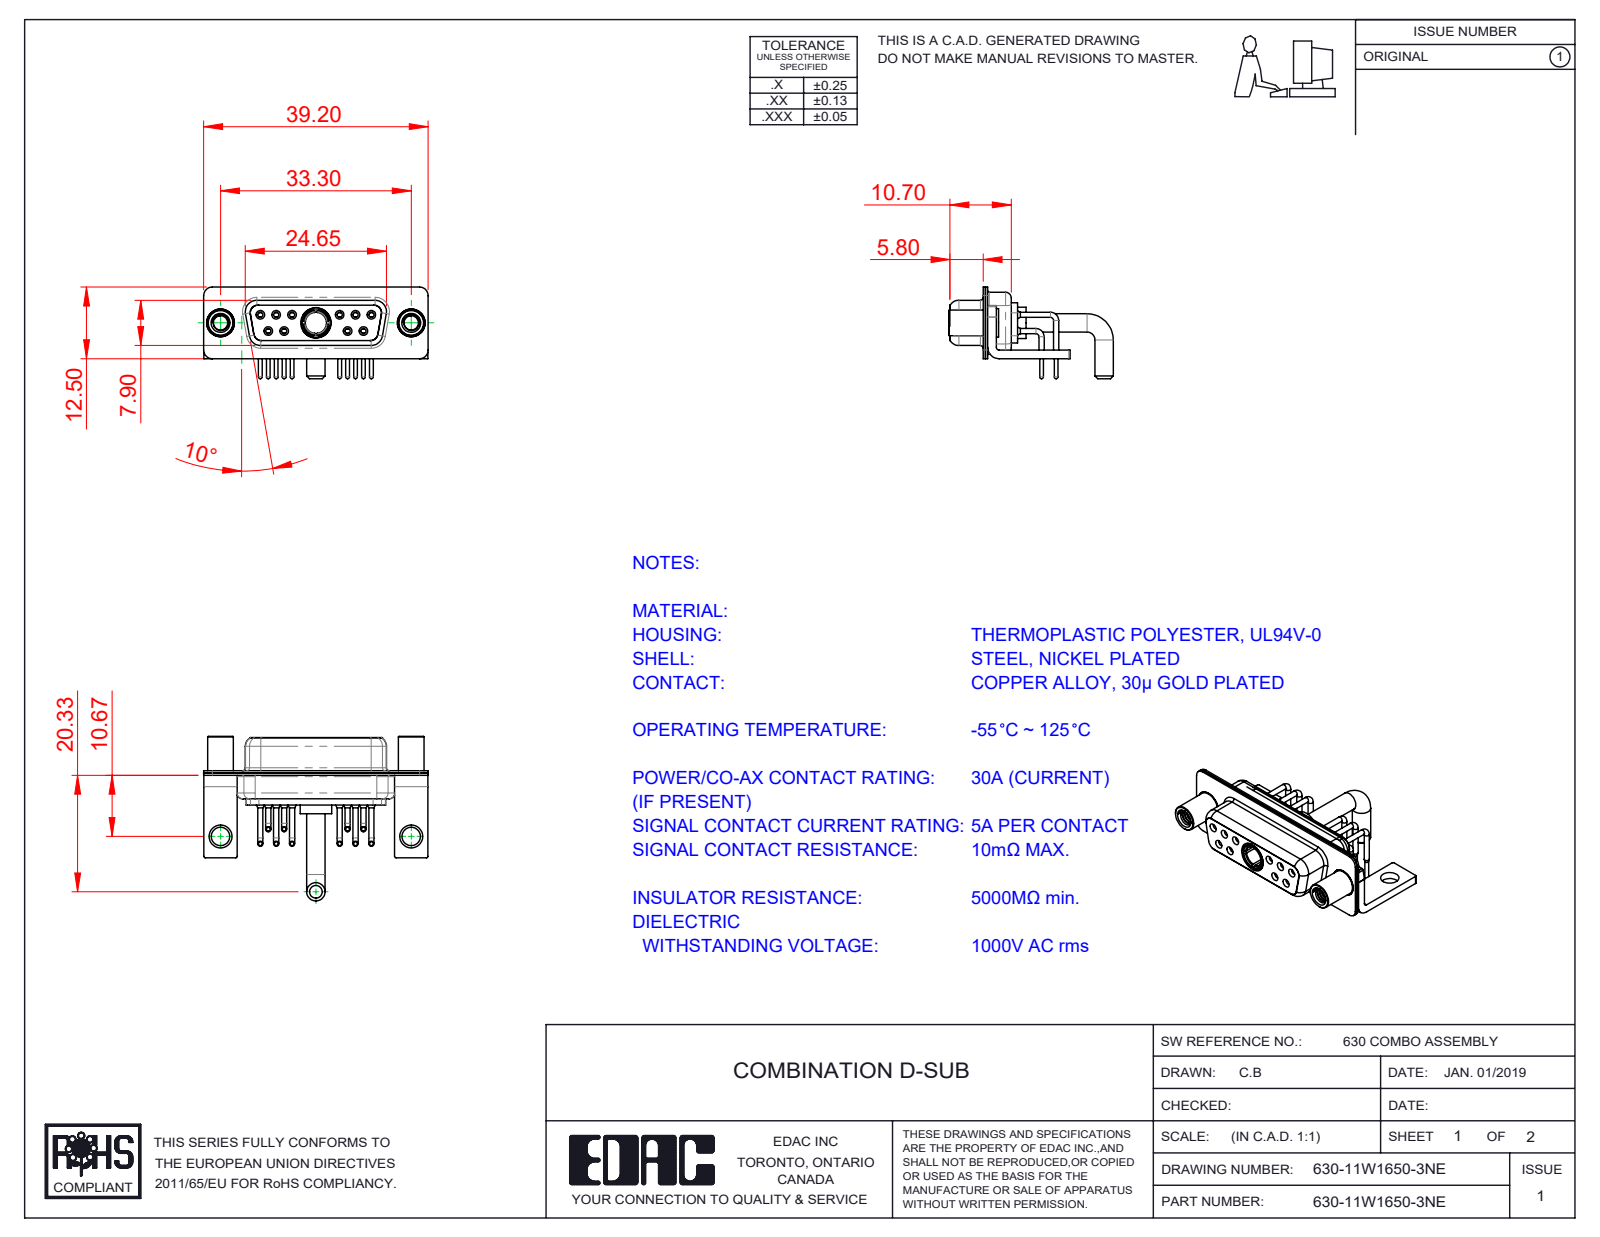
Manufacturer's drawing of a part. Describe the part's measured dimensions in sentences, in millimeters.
The part is named "630Combo Shell Rear_15 Contacts; 630Combo Stabilizer Bracket; Power Socket_Ext 30A RA; 630Combo Contact Row 2 (+5 more)". Its 3-D file was written by "SolidWorks 2020 (CONFIG_CONTROL_DESIGN)". It is 19 solids with 985 faces: 268 planar, 464 cylindrical and 253 other. Overall it measures 39.2 by 28.73 by 16 millimeters. Its volume is 3 115 cubic millimeters and its surface area 7 286 square millimeters. Round holes: 10 of diameter 0.9, 10 of diameter 1.1, 10 of diameter 1.5, 10 of diameter 2, 6 of diameter 1.7, 4 of diameter 1.6, 3 of diameter 4.85, 2 of diameter 2.5, 2 of diameter 3.2, 2 of diameter 4, 2 of diameter 4.05, 1 of diameter 3.7. Round bosses or shafts: 10 of diameter 0.9, 10 of diameter 0.65, 6 of diameter 1.6, 2 of diameter 5, 2 of diameter 4.95, 2 of diameter 4.8, 2 of diameter 4.5, 2 of diameter 3.2. Partial cylindrical surfaces (rounded edges, fillets, slot ends): 16 of radius 0.25, 16 of radius 1.5, 13 of radius 2, 12 of radius 1.35, 8 of radius 1.6, 5 of radius 0.5, 4 of radius 0.6, 4 of radius 0.65. The main face-to-face distances are 0.4, 0.8, 1.4, 0.45, 8.45, 1.5, 1.8, 8.9, 6.2, 2.3. The hole center spacings are 3.16, 2.77, 13.85, 11.08, 16.62, 5.03, 5.04, 5.54.
